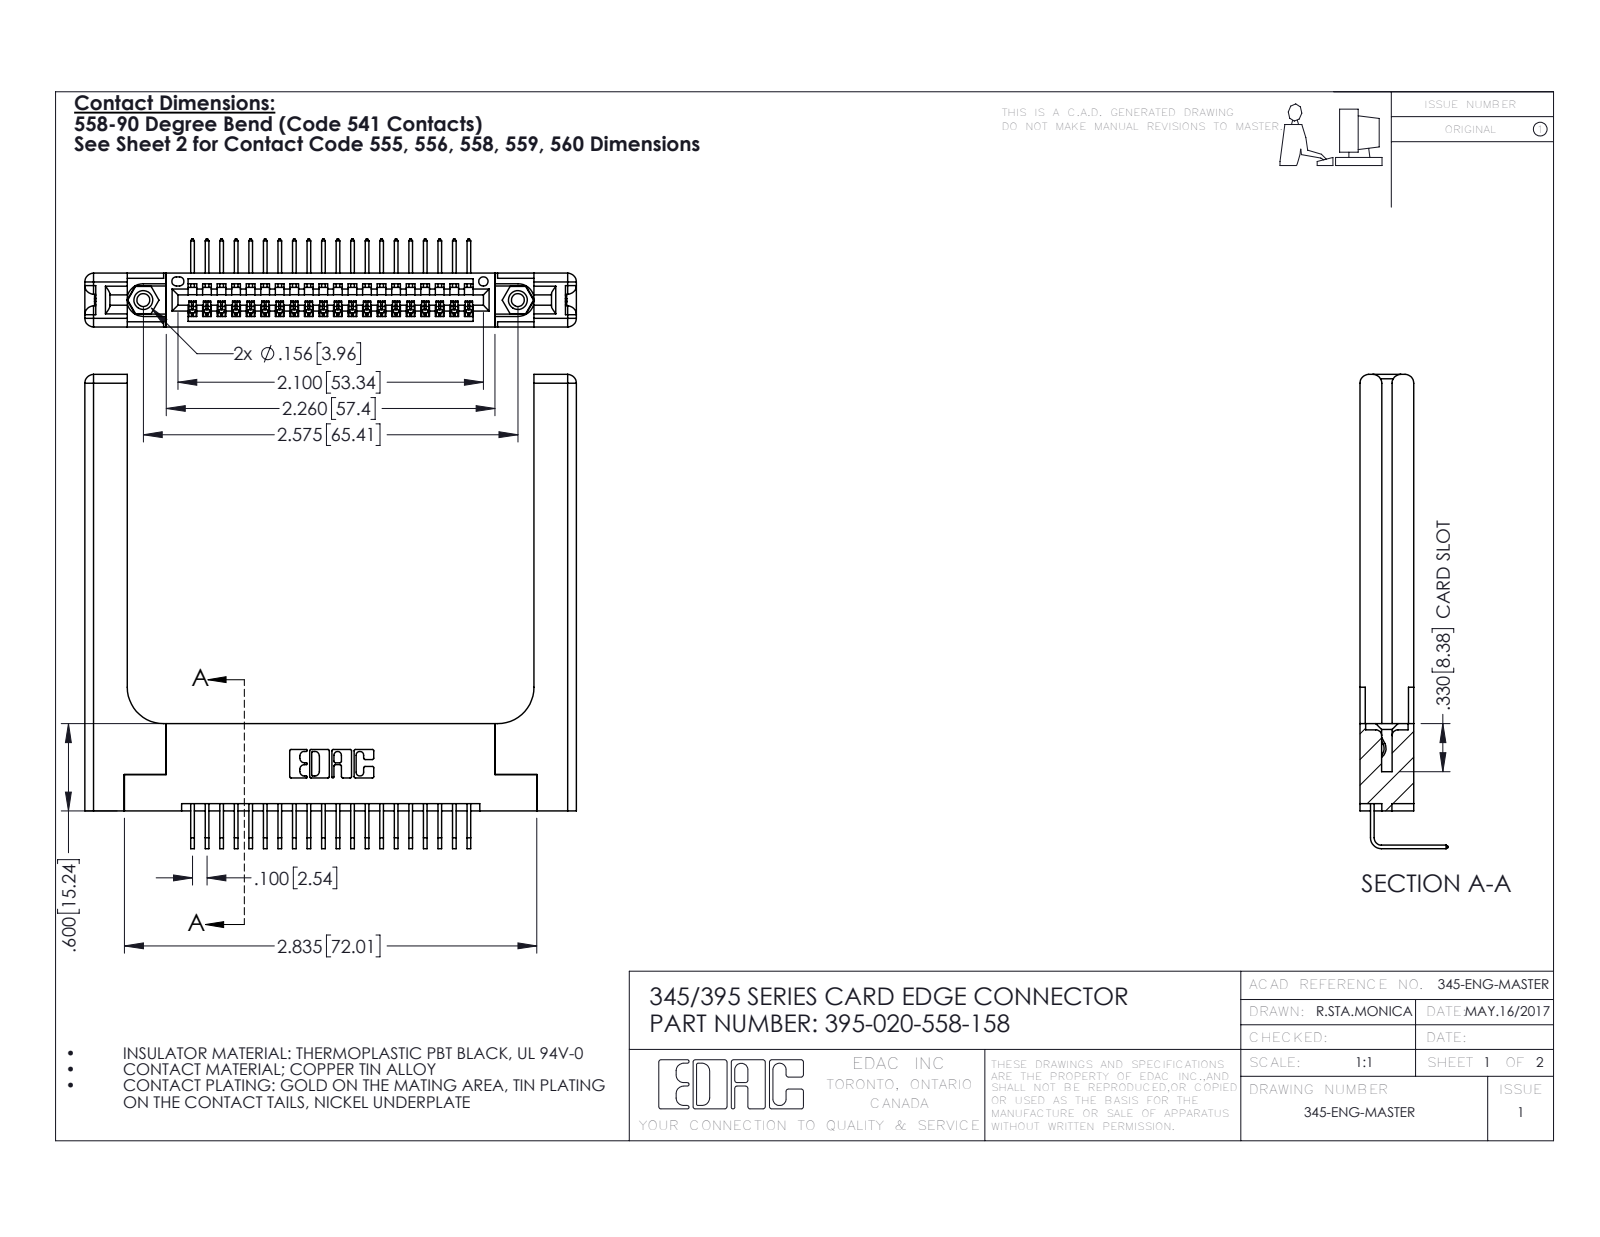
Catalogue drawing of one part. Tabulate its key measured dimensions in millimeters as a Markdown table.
| quantity | value |
| --- | --- |
| part name | 345-292-001_558 Tail - 2; 345-220-058_345-220-058; 345 Part_Flush Mounting Lugs - 0.156 Dia-TH; 395-020-558-158 (+1 more) |
| STEP written by | SolidWorks 2016 (CONFIG_CONTROL_DESIGN) |
| units | millimeters |
| bodies | 25 solids, 1582 faces (1068 planar, 454 cylindrical, 60 other) |
| overall size | 85.8 × 82.8 × 15.4 |
| volume | 16 550 mm³ |
| surface area | 16 080 mm² |
| round holes (diameter × count) | 2.3 × 2, 3.2 × 2, 4 × 2, 1.6 × 1 |
| round bosses / shafts (diameter × count) | 3.9 × 2 |
| partial cylindrical surfaces (radius × count) | 0.2 × 40, 0.3 × 22, 1.5 × 16, 0.2 × 6, 0.8 × 6, 0.7 × 3, 0.8 × 2, 0.8 × 2 |
| main face-to-face distances | 9.4, 1.8, 7.6, 5.1, 3.8, 3.8, 2, 5.6, 2.5, 6.9 |
| hole center spacings | 6.9, 59.5, 65.4 |
